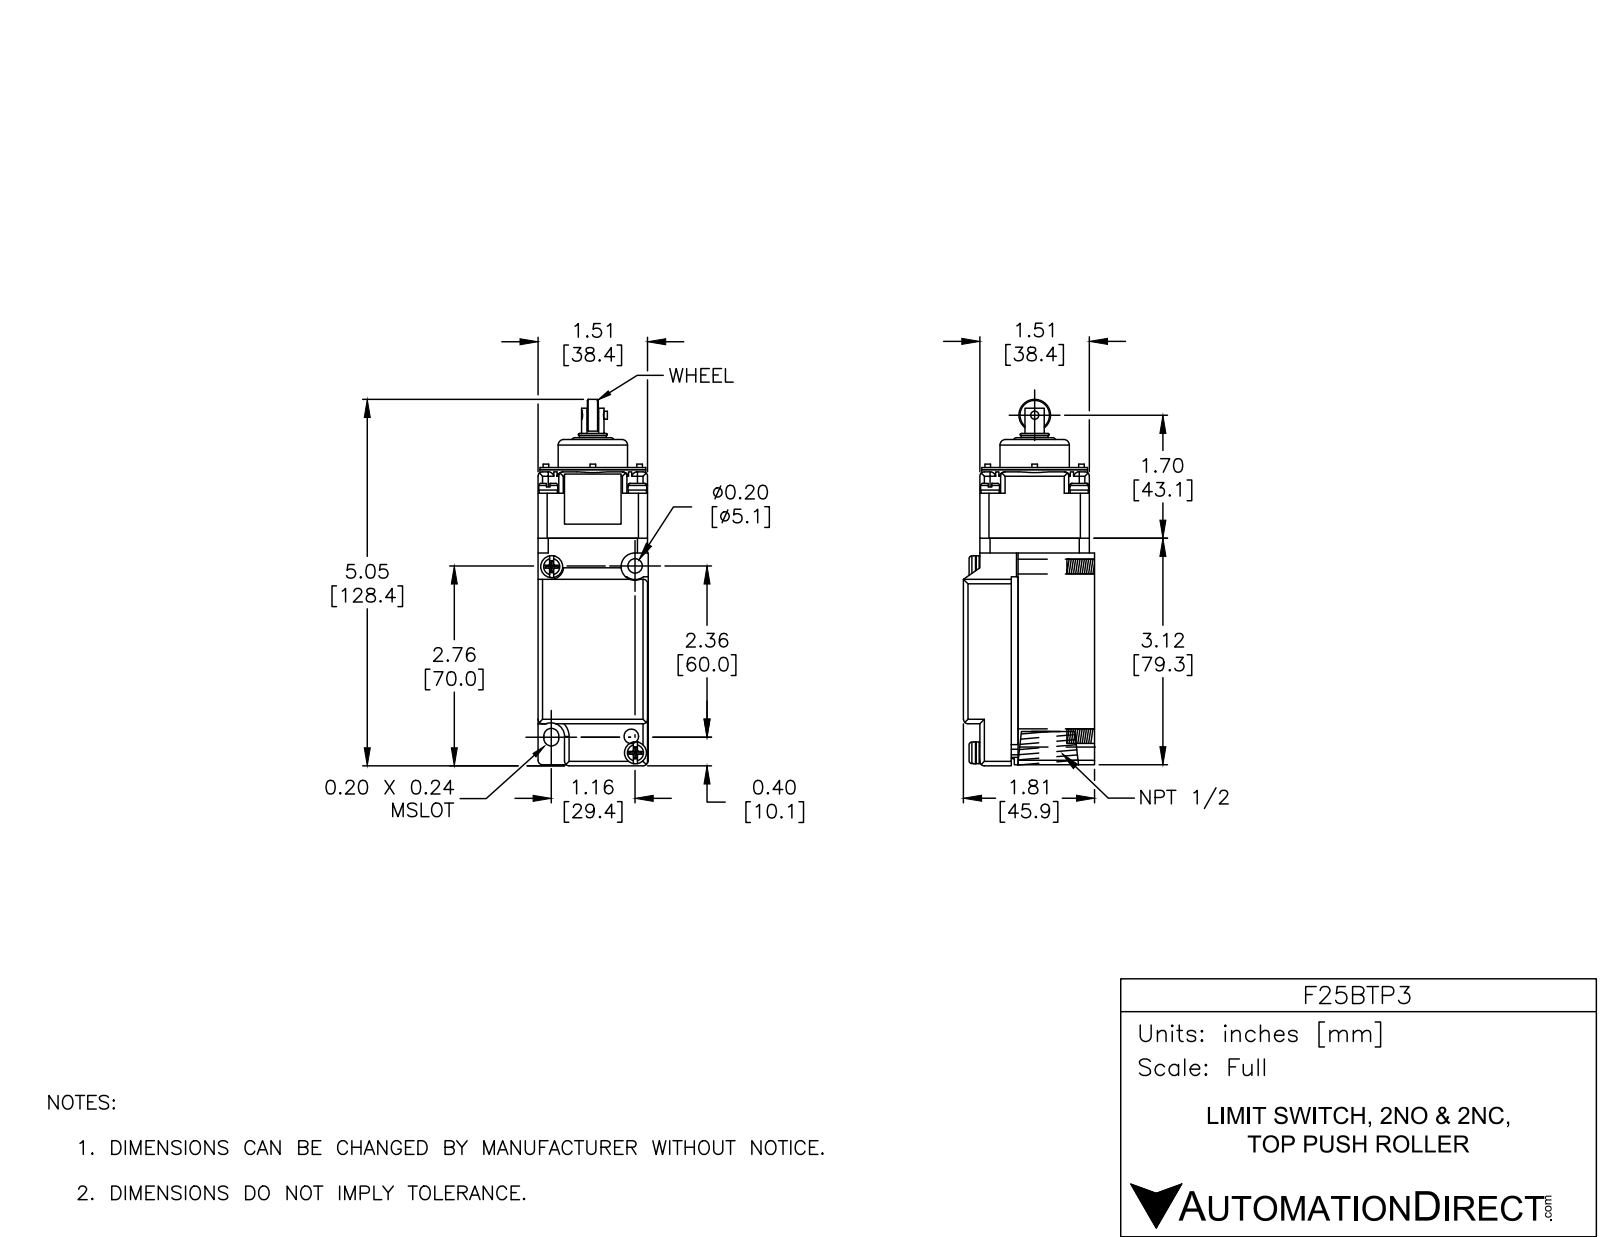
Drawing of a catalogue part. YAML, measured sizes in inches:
part_name: "F25BTP3"
step_written_by: "SolidWorks 2018 (AUTOMOTIVE_DESIGN)"
units: inches
bodies: {solids: 16, faces: 652, planar: 260, cylindrical: 143, other: 249}
overall_size: [5.054, 1.809, 1.52]
volume: 9.987
surface_area: 75.54
round_holes:
  - {diameter: 0.077, count: 4}
  - {diameter: 0.177, count: 4}
  - {diameter: 0.19, count: 3}
  - {diameter: 0.2, count: 3}
  - {diameter: 0.094, count: 1}
  - {diameter: 0.096, count: 1}
  - {diameter: 0.13, count: 1}
  - {diameter: 0.23, count: 1}
  - {diameter: 0.92, count: 1}
  - {diameter: 1.054, count: 1}
round_bosses_or_shafts:
  - {diameter: 0.25, count: 5}
  - {diameter: 0.26, count: 4}
  - {diameter: 0.14, count: 4}
  - {diameter: 0.302, count: 2}
  - {diameter: 0.3, count: 2}
  - {diameter: 1.458, count: 1}
  - {diameter: 0.956, count: 1}
  - {diameter: 0.437, count: 1}
partial_cylinders:
  - {radius: 0.062, count: 21}
  - {radius: 0.03, count: 16}
  - {radius: 0.015, count: 8}
  - {radius: 0.062, count: 8}
  - {radius: 0.14, count: 4}
  - {radius: 0.145, count: 4}
  - {radius: 0.102, count: 2}
  - {radius: 0.188, count: 2}
face_to_face_distances: [0.094, 1.149, 1.055, 1.52, 0.945, 0.66, 0.754, 1.809, 1.51, 0.227]
hole_center_spacings: [1.403, 0.616, 0.646, 0.616, 0.87, 0.87, 0.913, 0.914]
